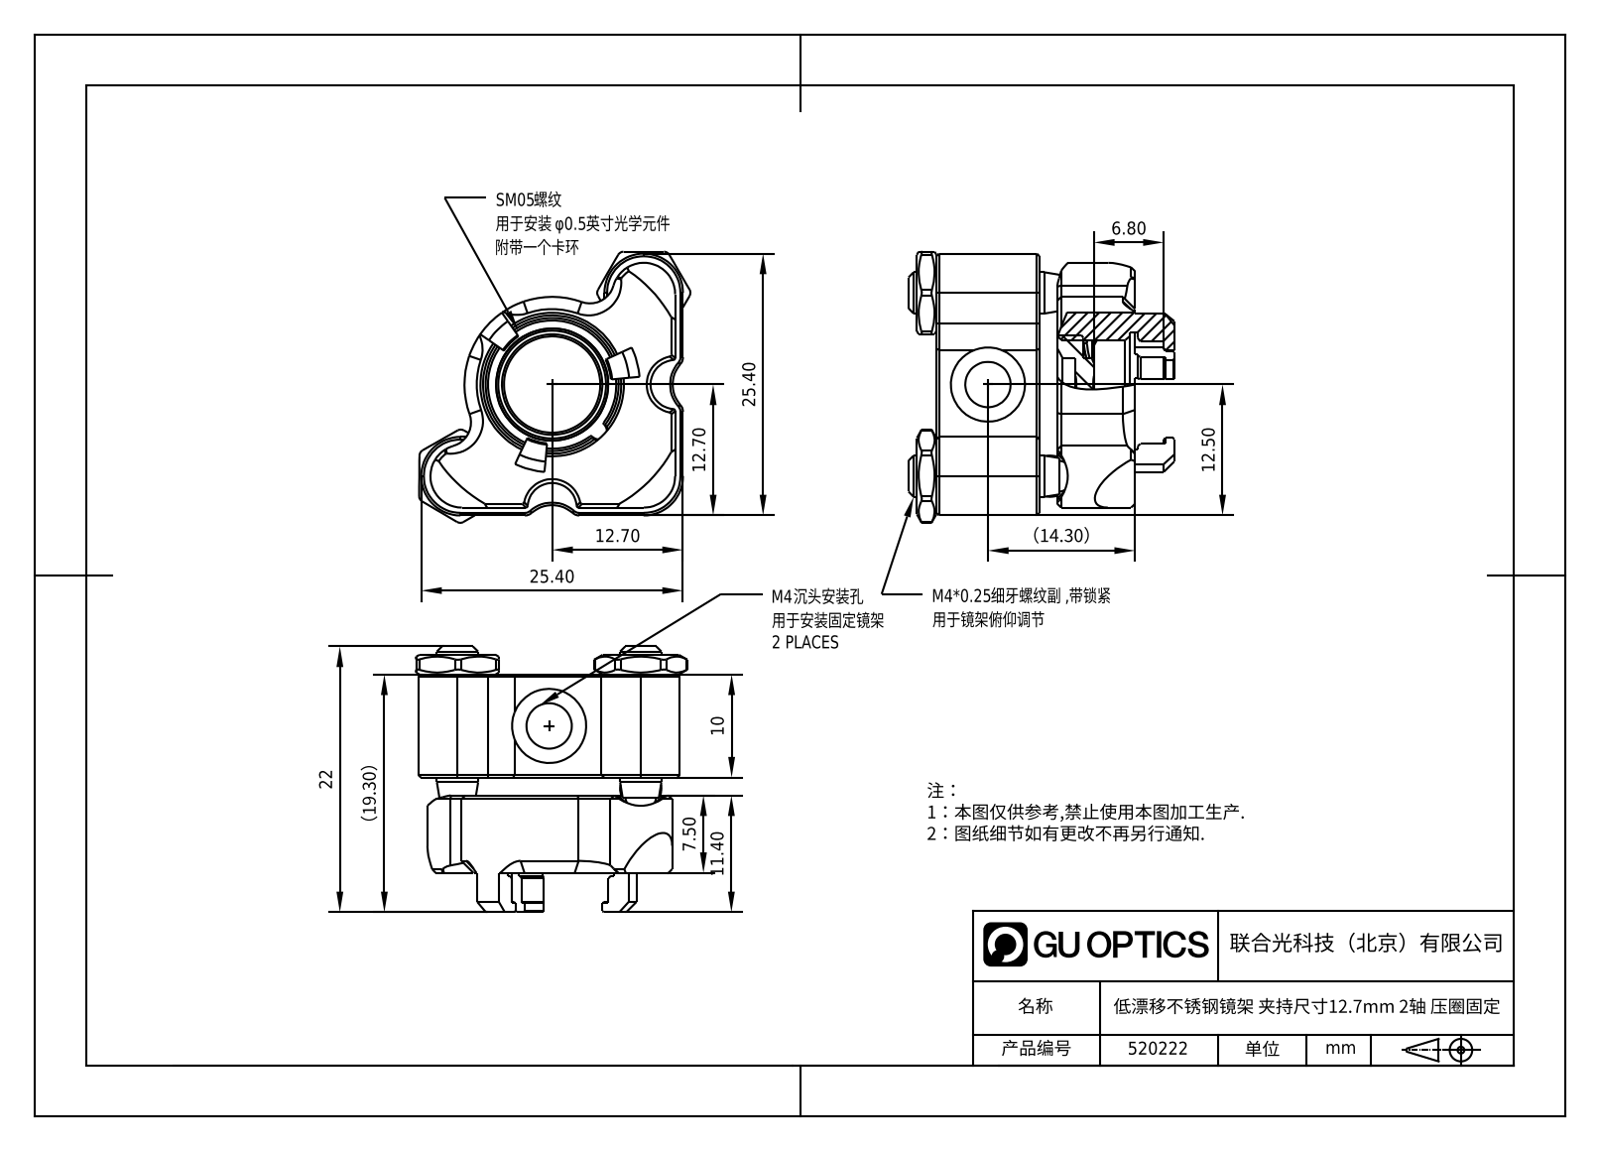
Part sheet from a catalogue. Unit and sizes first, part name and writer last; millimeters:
Units: millimetres
Overall size (bounding box): 26.33 × 26.31 × 25.79
Round holes (diameter × count): ⌀3.4 ×5, ⌀1.6 ×4, ⌀2 ×2, ⌀2.99 ×2, ⌀3.75 ×2, ⌀4 ×2, ⌀4.35 ×2, ⌀4.4 ×2, ⌀7.2 ×2, ⌀11.19 ×1, ⌀12.9 ×1, ⌀13.92 ×1
Round bosses / shafts (diameter × count): ⌀2.5 ×6, ⌀2 ×2, ⌀13.59 ×1
Partial cylindrical surfaces — rounded edges, fillets, slot ends (radius × count): R0.6 ×12, R1 ×8, R3.05 ×3, R3.81 ×3, R0.19 ×2, R0.19 ×2, R2.38 ×2, R2.39 ×2
Main face-to-face distances: 10, 9.27, 19.27, 11.73, 7.54, 1.73, 2, 0.76, 0.77, 5.62
Hole centre spacings: 9.72, 7.87, 11.49, 18.46, 21.93, 4.95, 5, 7.01
Volume: 4 380 mm³ · Surface area: 5 403 mm²
Bodies: 18 solids, 527 faces (173 planar, 153 cylindrical, 201 other)
Part name (STEP PRODUCT): 36.1，440c不锈钢滚珠_36.1.6_GZ-B4; ZFK不锈钢透镜卡环压圈_1.8.9.1_ZFKS-K05; 标准细牙锁紧螺母，外六角_3.2.6.19_DXJ-S0425-0802; DXS-0425标准型六角调节器 _3.2.2.3.1-DXS-0425-16 (+5 more)
STEP written by: SolidWorks 2021 (CONFIG_CONTROL_DESIGN)
